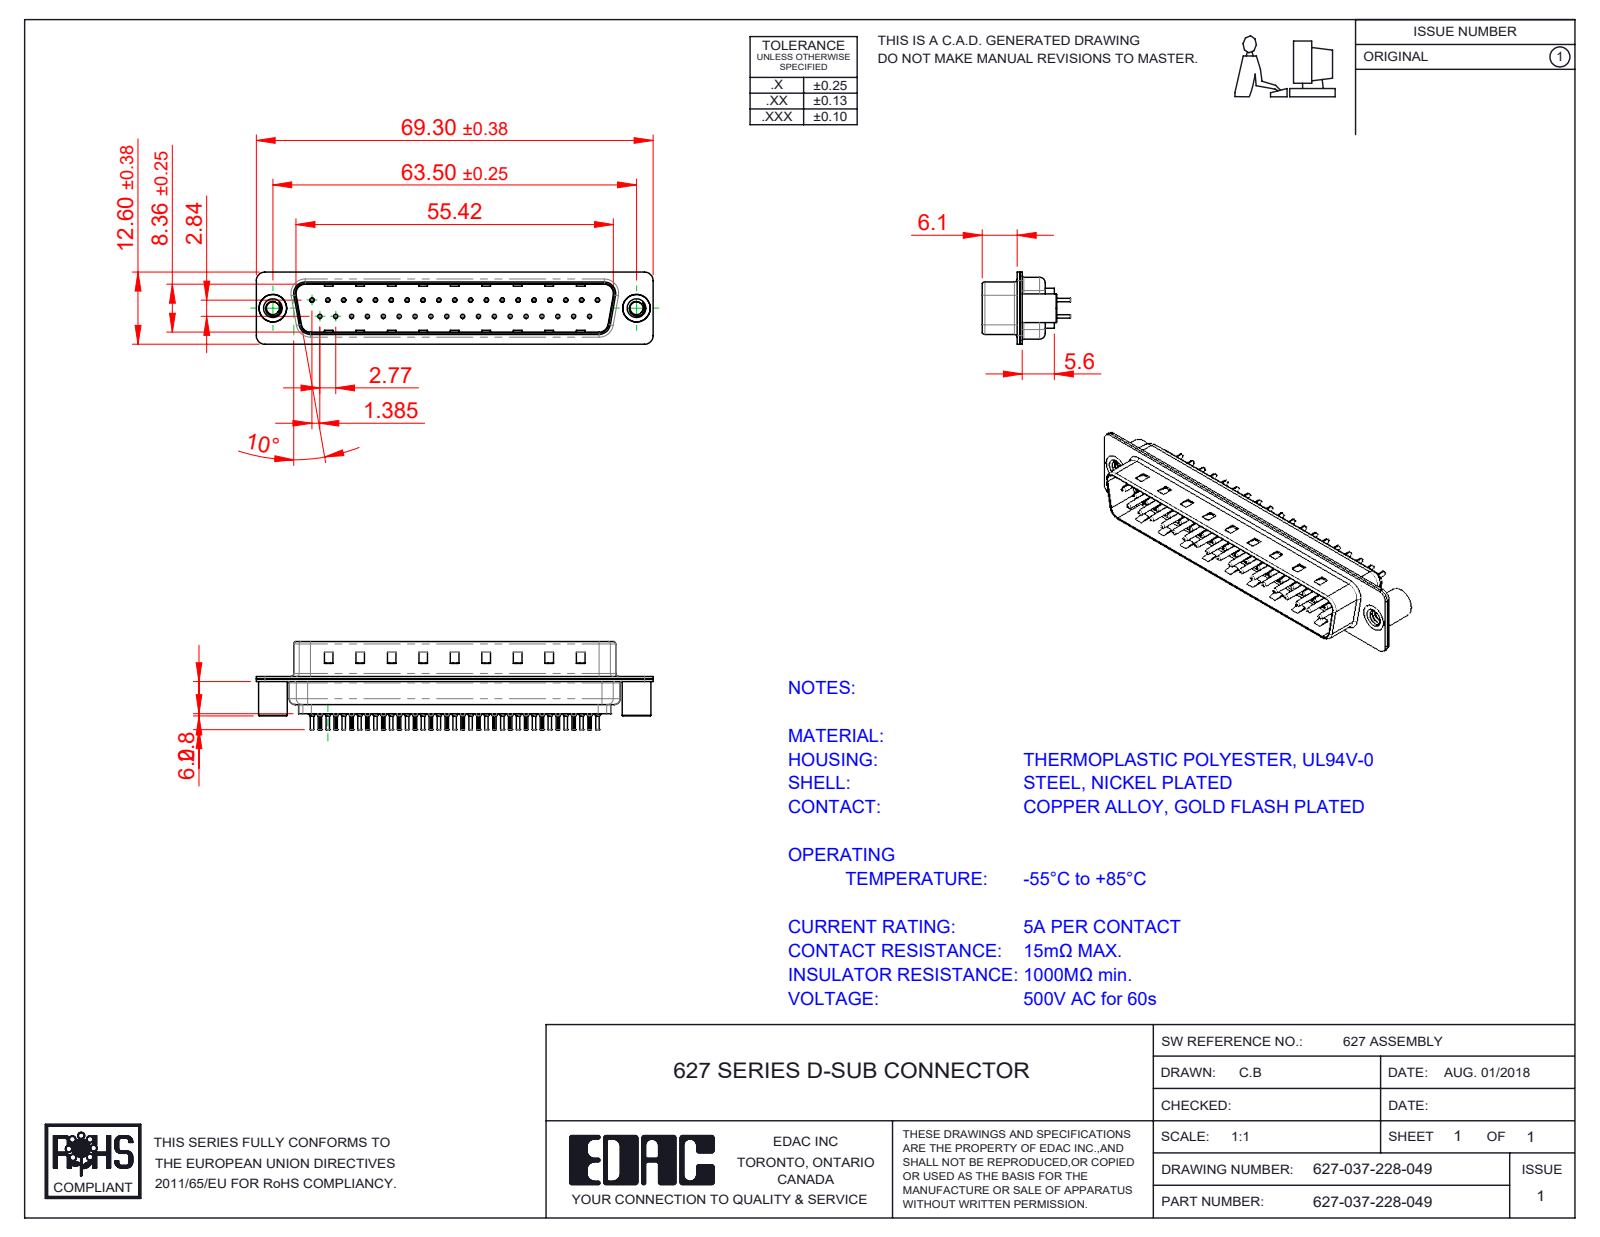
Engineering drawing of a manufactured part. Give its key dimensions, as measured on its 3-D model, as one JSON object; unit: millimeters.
{"part_name": "627-037-228-049; 627 Contact Row 1_28L; 627 Shell Rear_37 Contacts; 627 Contact Row 2_28L (+3 more)", "step_written_by": "SolidWorks 2020 (CONFIG_CONTROL_DESIGN)", "units": "millimeters", "bodies": {"solids": 43, "faces": 4145, "planar": 1097, "cylindrical": 1609, "other": 1439}, "overall_size": [69.3, 18.8, 12.6], "volume_mm3": 4652, "surface_area_mm2": 12486, "round_holes": [[0.2, 37], [0.35, 37], [1.1, 37], [1.6, 37], [2.26, 2], [4, 2], [4.8, 2]], "round_bosses_or_shafts": [[2, 37], [1.5, 37], [0.75, 37], [0.6, 37], [5, 2], [4.9, 2]], "partial_cylinders_radius": [[0.1, 74], [1.5, 16], [2, 12], [0.5, 8], [1.6, 8], [0.25, 4], [0.6, 4], [0.65, 4]], "face_to_face_distances": [0.4, 6.05, 0.82, 9.58, 0.45, 8.4, 0.68, 7.68, 1.5, 1.08], "hole_center_spacings": [3.16, 2.77, 5.54, 8.31, 5.04, 10.1, 11.08, 12.78]}
